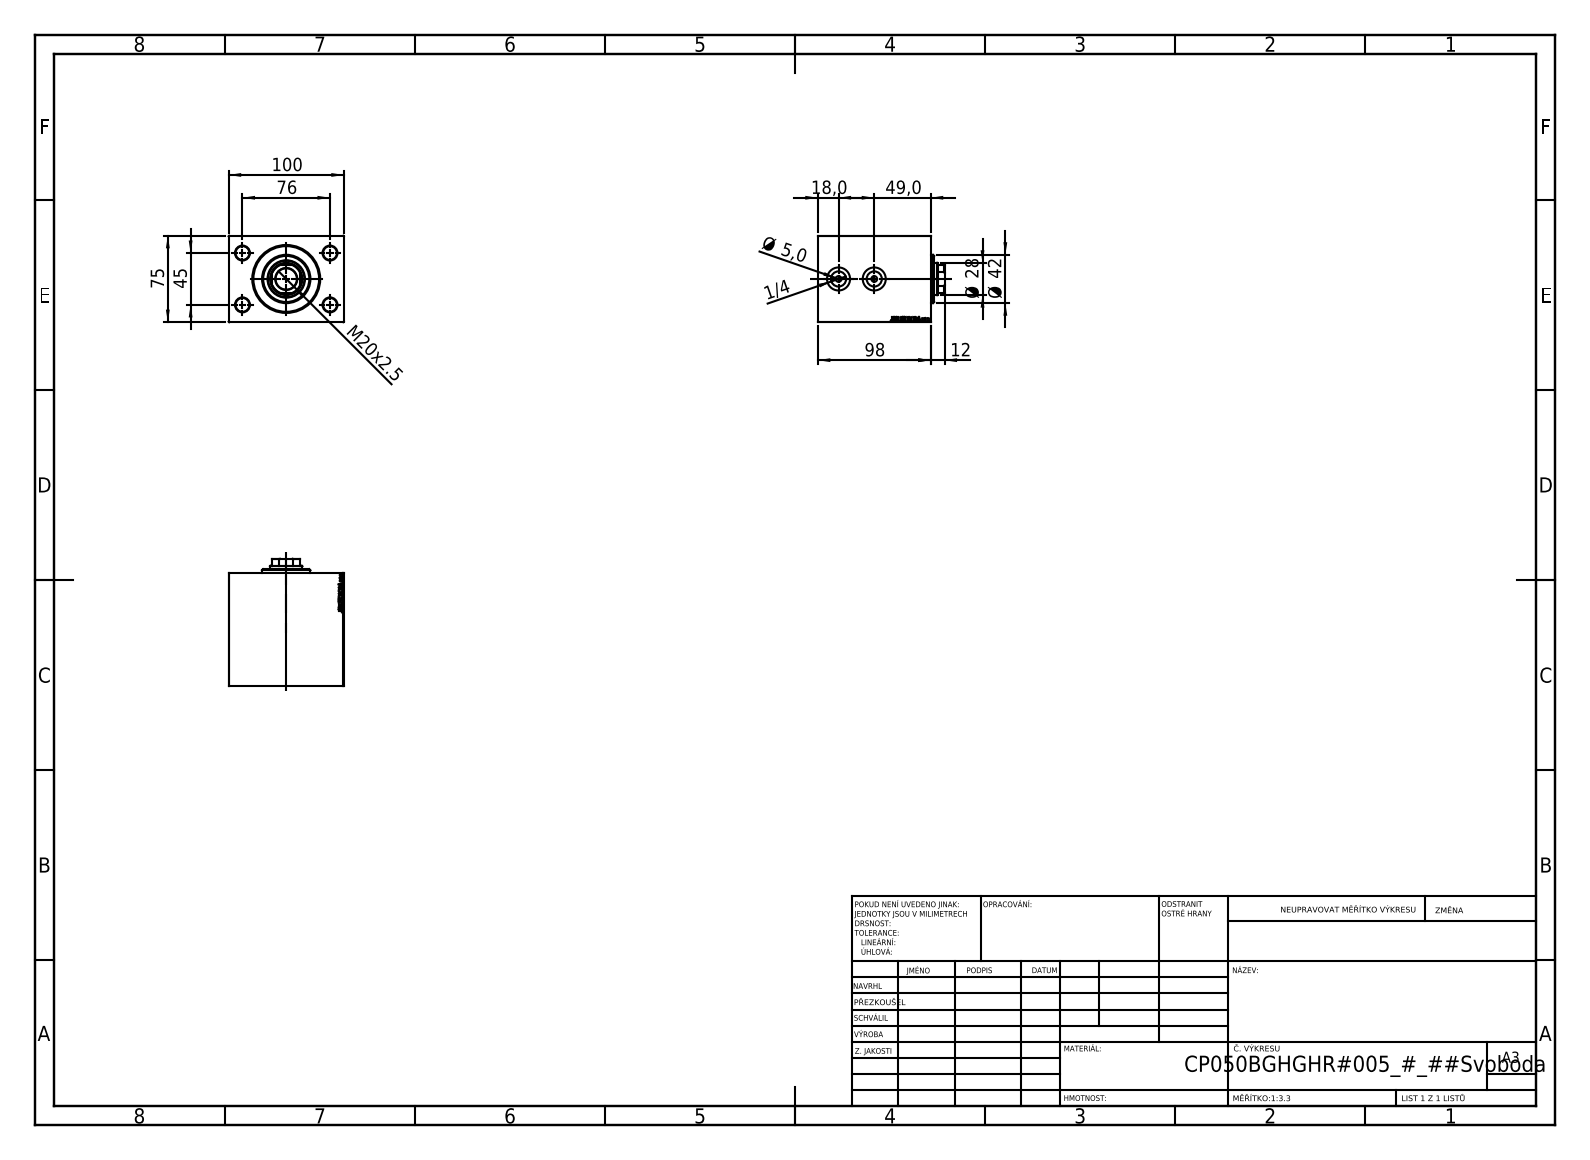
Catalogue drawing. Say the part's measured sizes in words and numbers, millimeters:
The part is named "V450CP_B_VCP; V450CP_VC_B; V450CP_B". Its 3-D file was written by "SolidWorks 2019 (CONFIG_CONTROL_DESIGN)". It is 3 solids with 904 faces: 406 planar, 68 cylindrical and 430 other. Overall it measures 110 by 100 by 75 millimeters. Its volume is 705 053 cubic millimeters and its surface area 103 585 square millimeters. Round holes: 4 of diameter 12, 2 of diameter 4, 2 of diameter 5, 2 of diameter 9.73, 2 of diameter 13.16, 2 of diameter 15, 2 of diameter 20, 1 of diameter 18.5, 1 of diameter 28, 1 of diameter 31.5, 1 of diameter 32.5, 1 of diameter 50. Round bosses or shafts: 1 of diameter 42. Partial cylindrical surfaces (rounded edges, fillets, slot ends): 1 of radius 13.5. The main face-to-face distances are 75, 100, 98, 49, 14, 84, 44, 5, 35, 30. The hole center spacings are 44.16, 45, 76, 88.32, 31, 42.55.
